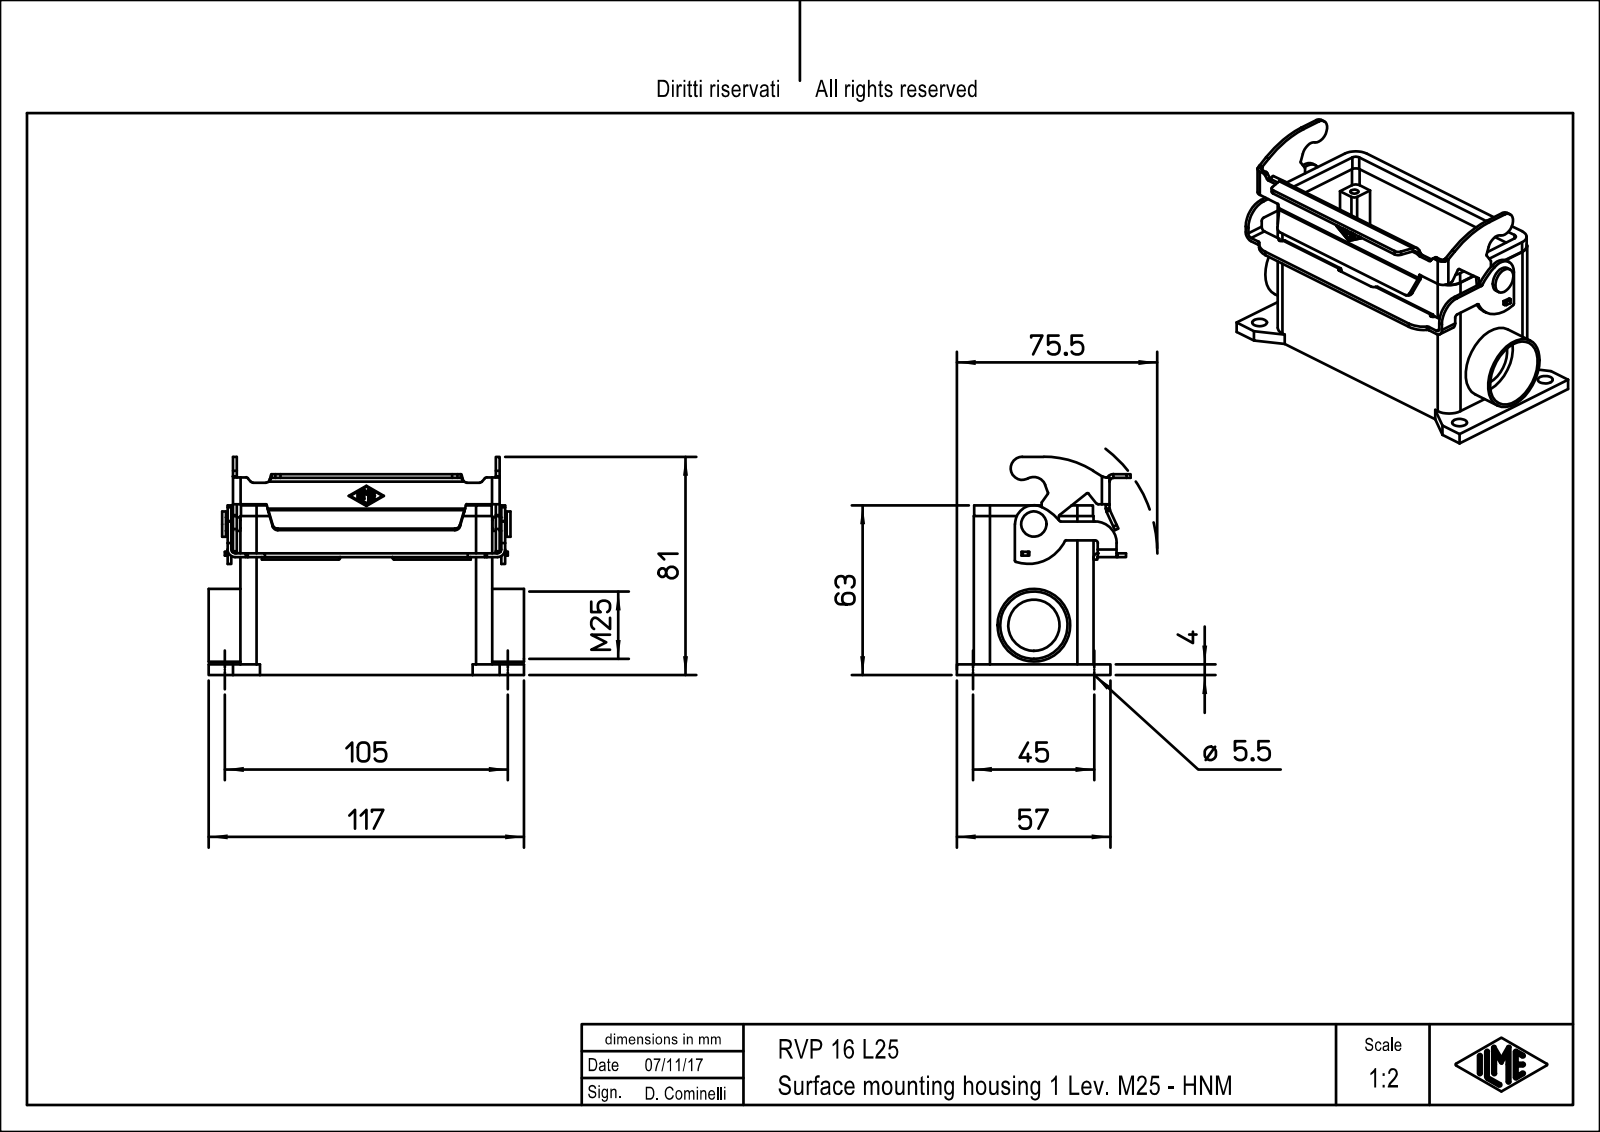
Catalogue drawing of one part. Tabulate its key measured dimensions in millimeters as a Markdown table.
| quantity | value |
| --- | --- |
| part name | RVP_16_L25 |
| STEP written by | PTC Creo Elements/Direct Modeling 19.0E 27-Jun-2016 (C) Parametric Technology GmbH (AUTOMOTIVE_DESIGN) |
| units | millimeters |
| bodies | 1 solid, 381 faces (199 planar, 170 cylindrical, 12 other) |
| overall size | 117 × 81 × 64.48 |
| volume | 105 272 mm³ |
| surface area | 59 294 mm² |
| round holes (diameter × count) | 2.46 × 4, 3 × 4, 5.5 × 4, 19 × 1, 25 × 1 |
| round bosses / shafts (diameter × count) | 27 × 1, 9.4 × 1, 5 × 1, 3 × 1 |
| partial cylindrical surfaces (radius × count) | 0.25 × 16, 0.5 × 12, 1 × 12, 1.5 × 11, 2 × 8, 1.4 × 6, 2.8 × 6, 1.8 × 4 |
| main face-to-face distances | 4, 40.5, 1.4, 44.5, 36.5, 2, 99.6, 11.5, 82, 6.75 |
| hole center spacings | 16.43, 38.54, 91.69, 98.09, 27, 45, 77.5, 82.07 |
